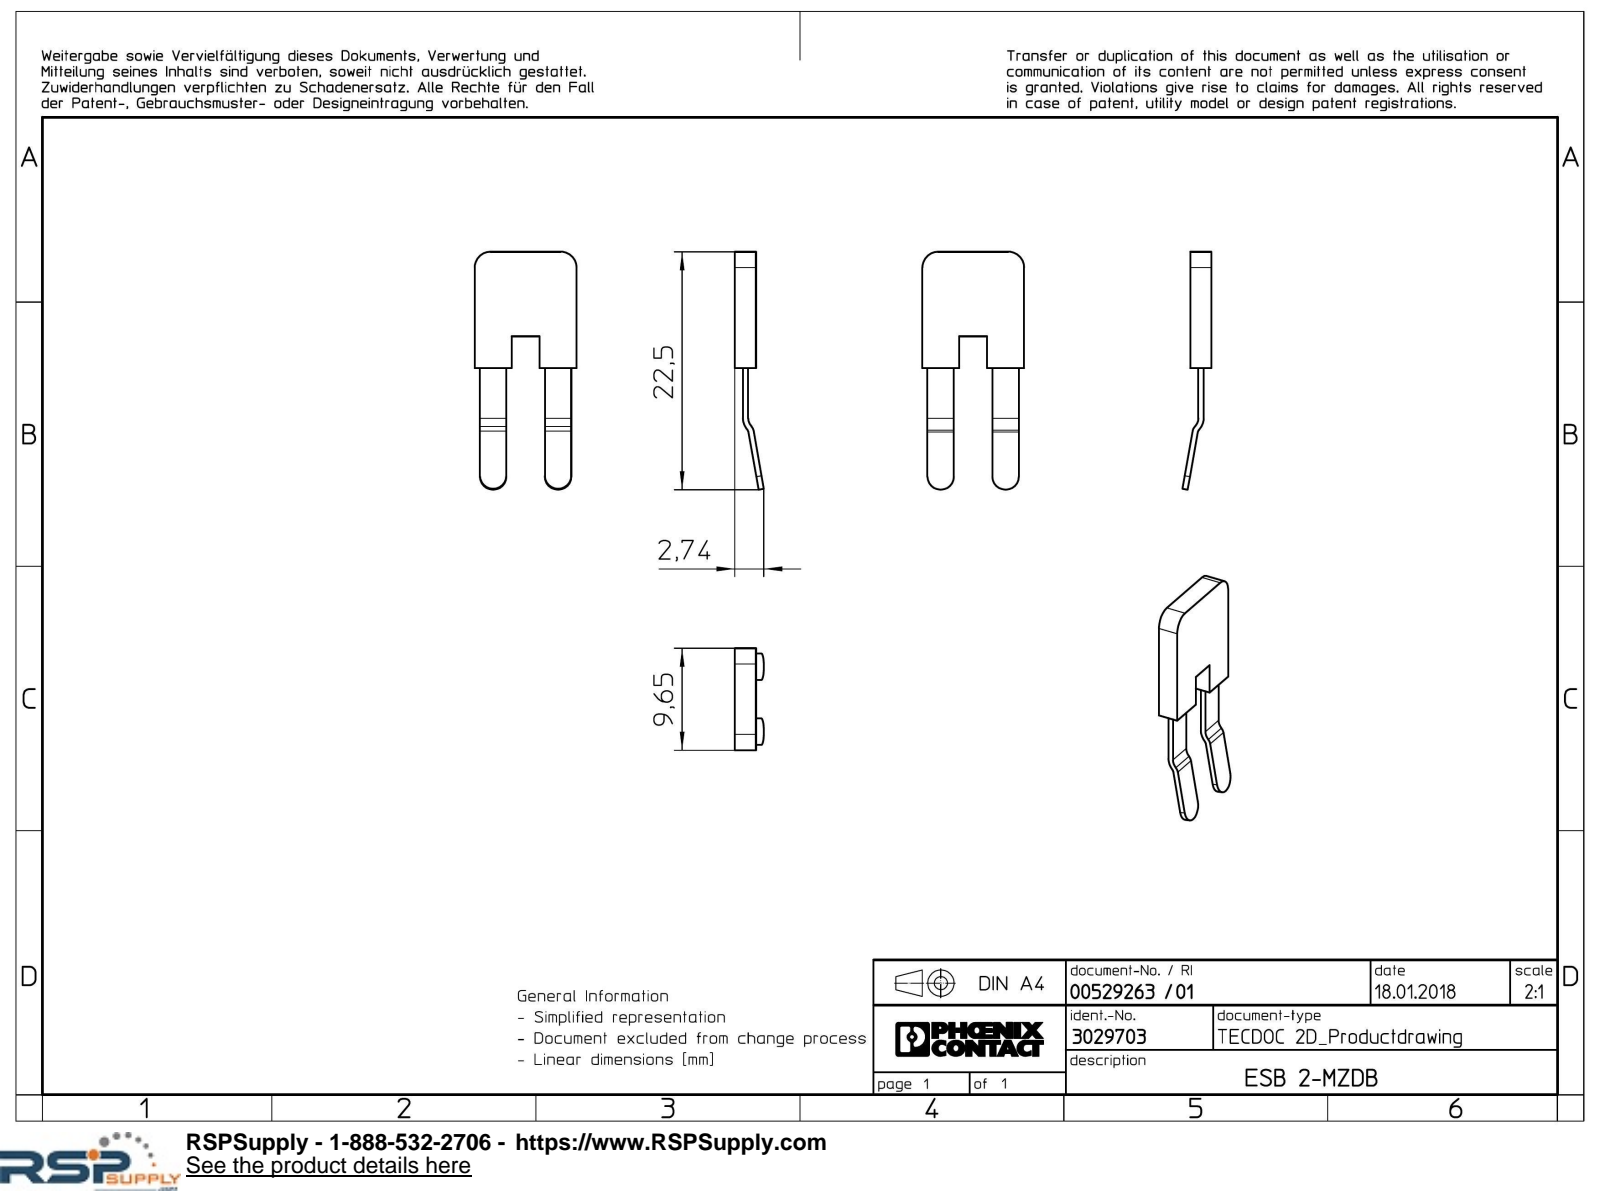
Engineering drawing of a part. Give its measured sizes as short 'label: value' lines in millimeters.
name: ESB_2-MZDB-select
written by: Creo Elements/Direct Modeling 18.1I 14-Aug-2016 (C) Parametric Technology GmbH (AUTOMOTIVE_DESIGN)
unit: mm
bodies: 1 solid, 34 faces (22 planar, 12 cylindrical, 0 other)
size: 22.5 × 9.65 × 2.74
volume: 223 mm³; area: 423 mm²
rounds: 2× R1.25, 2× R1.5, 1× R0.3, 1× R0.8, 1× R1.1, 1× R1.6
face distances: 2, 0.75, 1.25, 0.5, 0.49, 3, 6.15, 9.65, 3.5, 11
